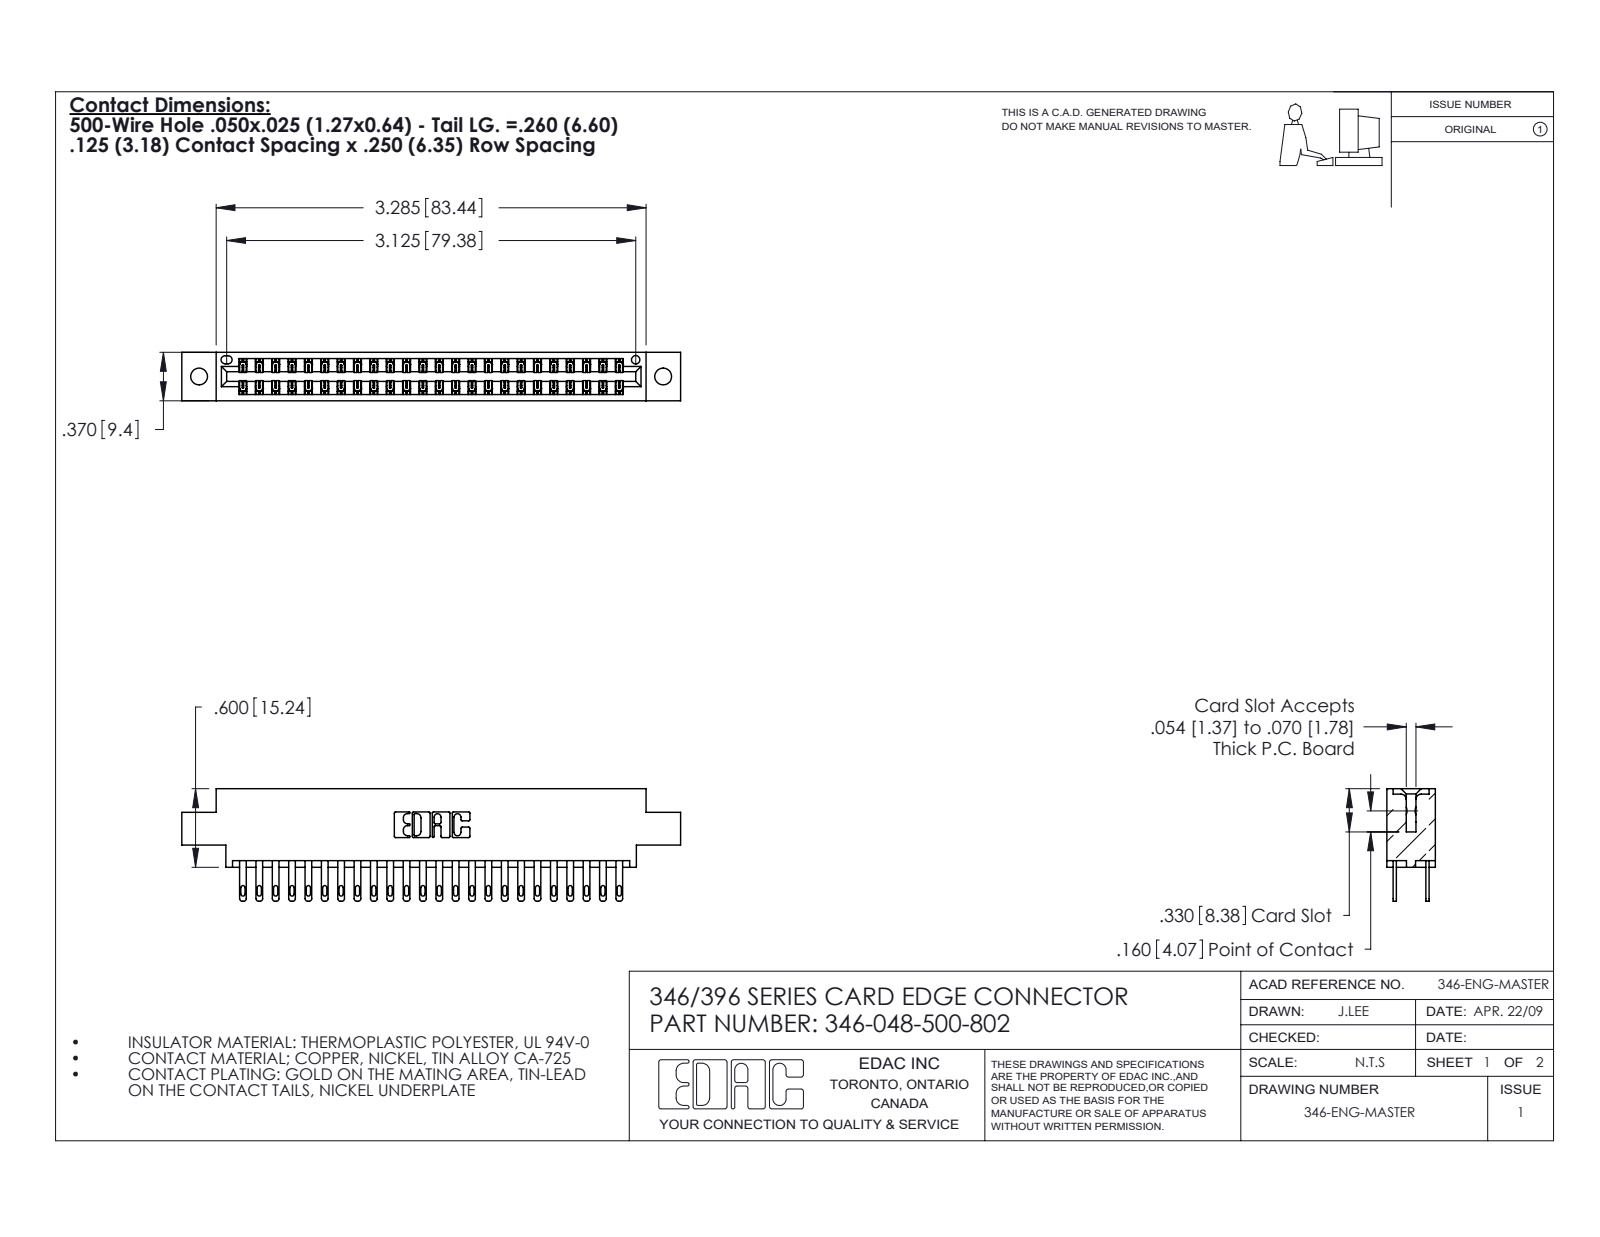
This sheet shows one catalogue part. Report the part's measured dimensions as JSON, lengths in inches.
{"part_name": "346 Part_0.170 Offset - 0.128 Dia; 346-048-500-802; 345-292-001_345-293-100", "step_written_by": "SolidWorks 2020 (CONFIG_CONTROL_DESIGN)", "units": "inches", "bodies": {"solids": 49, "faces": 2430, "planar": 1472, "cylindrical": 958, "other": 0}, "overall_size": [3.81, 0.86, 0.37], "volume_in3": 0.565, "surface_area_in2": 19.91, "round_holes": [[0.128, 2], [0.064, 1]], "partial_cylinders_radius": [[0.006, 72], [0.016, 48], [0.02, 48], [0.01, 22], [0.007, 6], [0.031, 6], [0.026, 3], [0.014, 2]], "face_to_face_distances": [0.048, 0.322, 0.25, 0.37, 0.072, 0.298, 0.025, 0.275, 0.148, 0.222], "hole_center_spacings": [0.246, 3.337, 3.545]}
